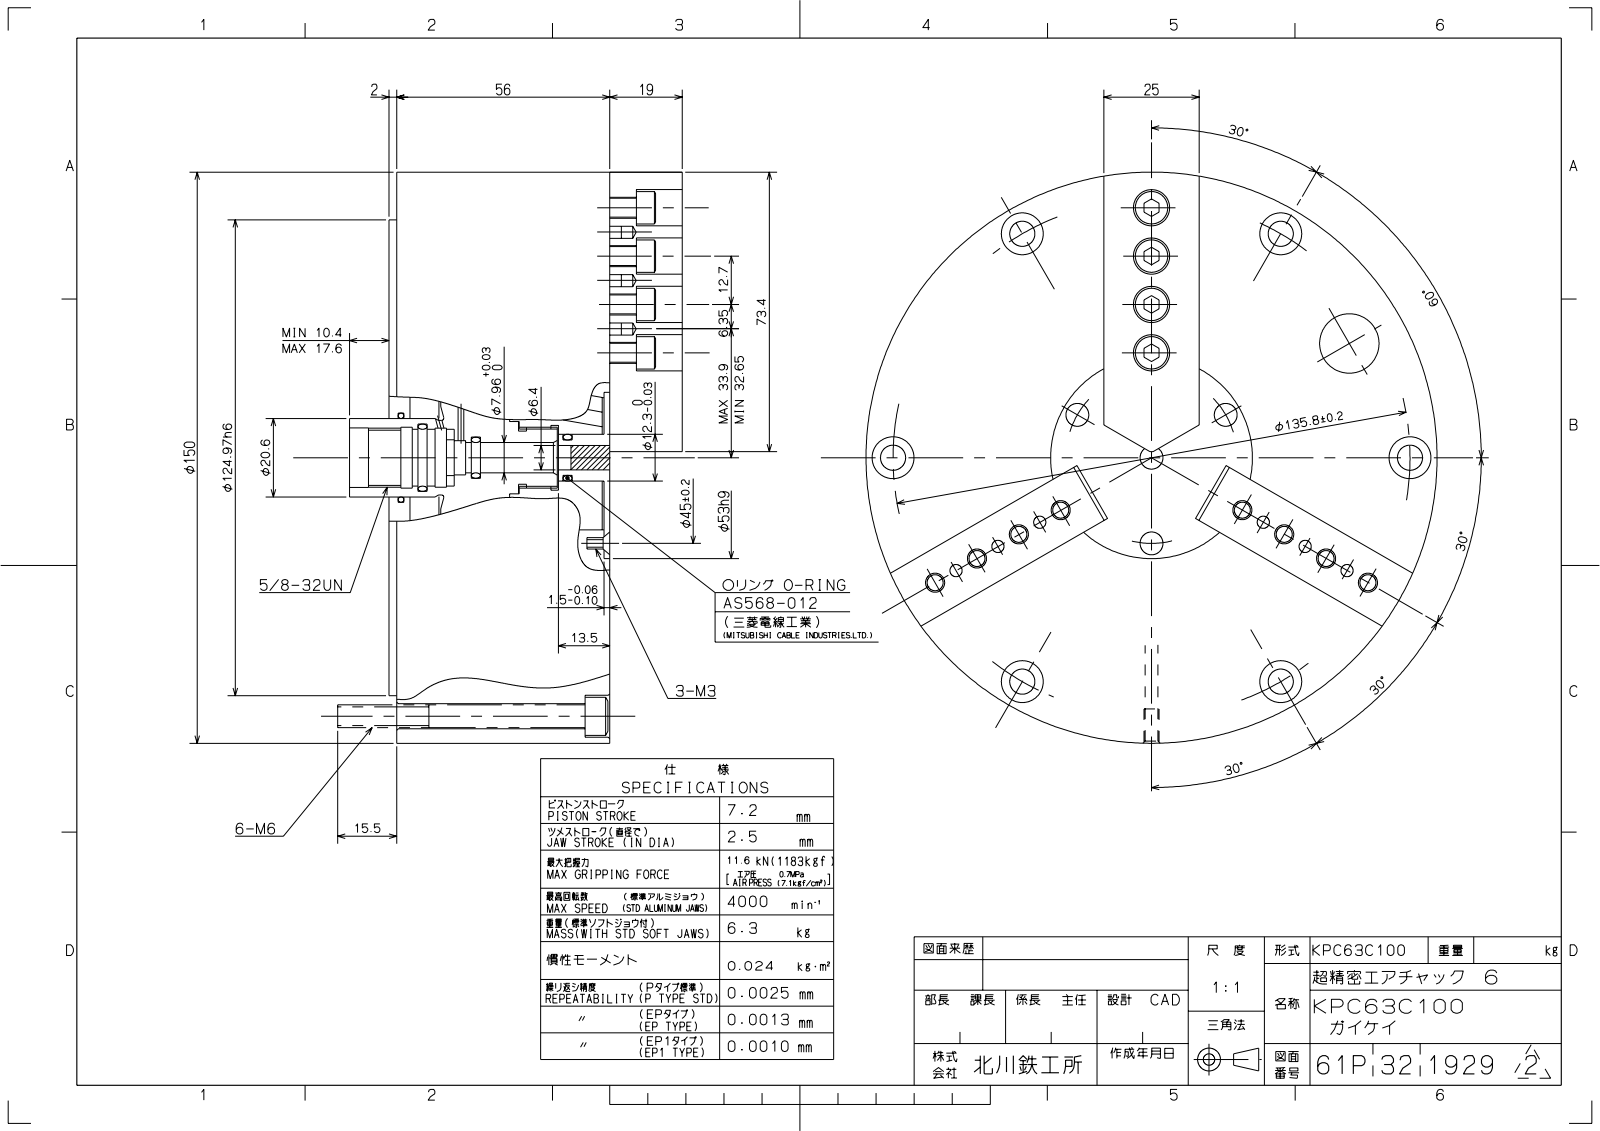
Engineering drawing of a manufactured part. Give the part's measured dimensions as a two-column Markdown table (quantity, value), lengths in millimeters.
| quantity | value |
| --- | --- |
| part name | KPC63C100 |
| STEP written by | ST-DEVELOPER v16.7 (AUTOMOTIVE_DESIGN) |
| units | millimeters |
| bodies | 1 solid, 815 faces (520 planar, 209 cylindrical, 86 other) |
| overall size | 150.05 × 150 × 87.4 |
| volume | 1 089 000 mm³ |
| surface area | 122 465 mm² |
| round holes (diameter × count) | 3 × 15, 5 × 12, 5.5 × 12, 10 × 12, 2.5 × 6, 3.3 × 6, 4 × 6, 4.5 × 6, 6.6 × 6, 8 × 6, 11 × 6, 6.3 × 3 |
| round bosses / shafts (diameter × count) | 8.5 × 12, 6 × 9, 10 × 6, 7 × 6, 2.69 × 3, 150 × 1, 124.97 × 1, 27 × 1 |
| partial cylindrical surfaces (radius × count) | 0.6 × 12, 75 × 3, 26.5 × 1 |
| main face-to-face distances | 58, 2, 56, 25, 19, 77, 75, 27, 28.75, 1.75 |
| hole center spacings | 6.35, 12.7, 19.05, 67.9, 25.4, 31.75, 33.95, 42.1 |
